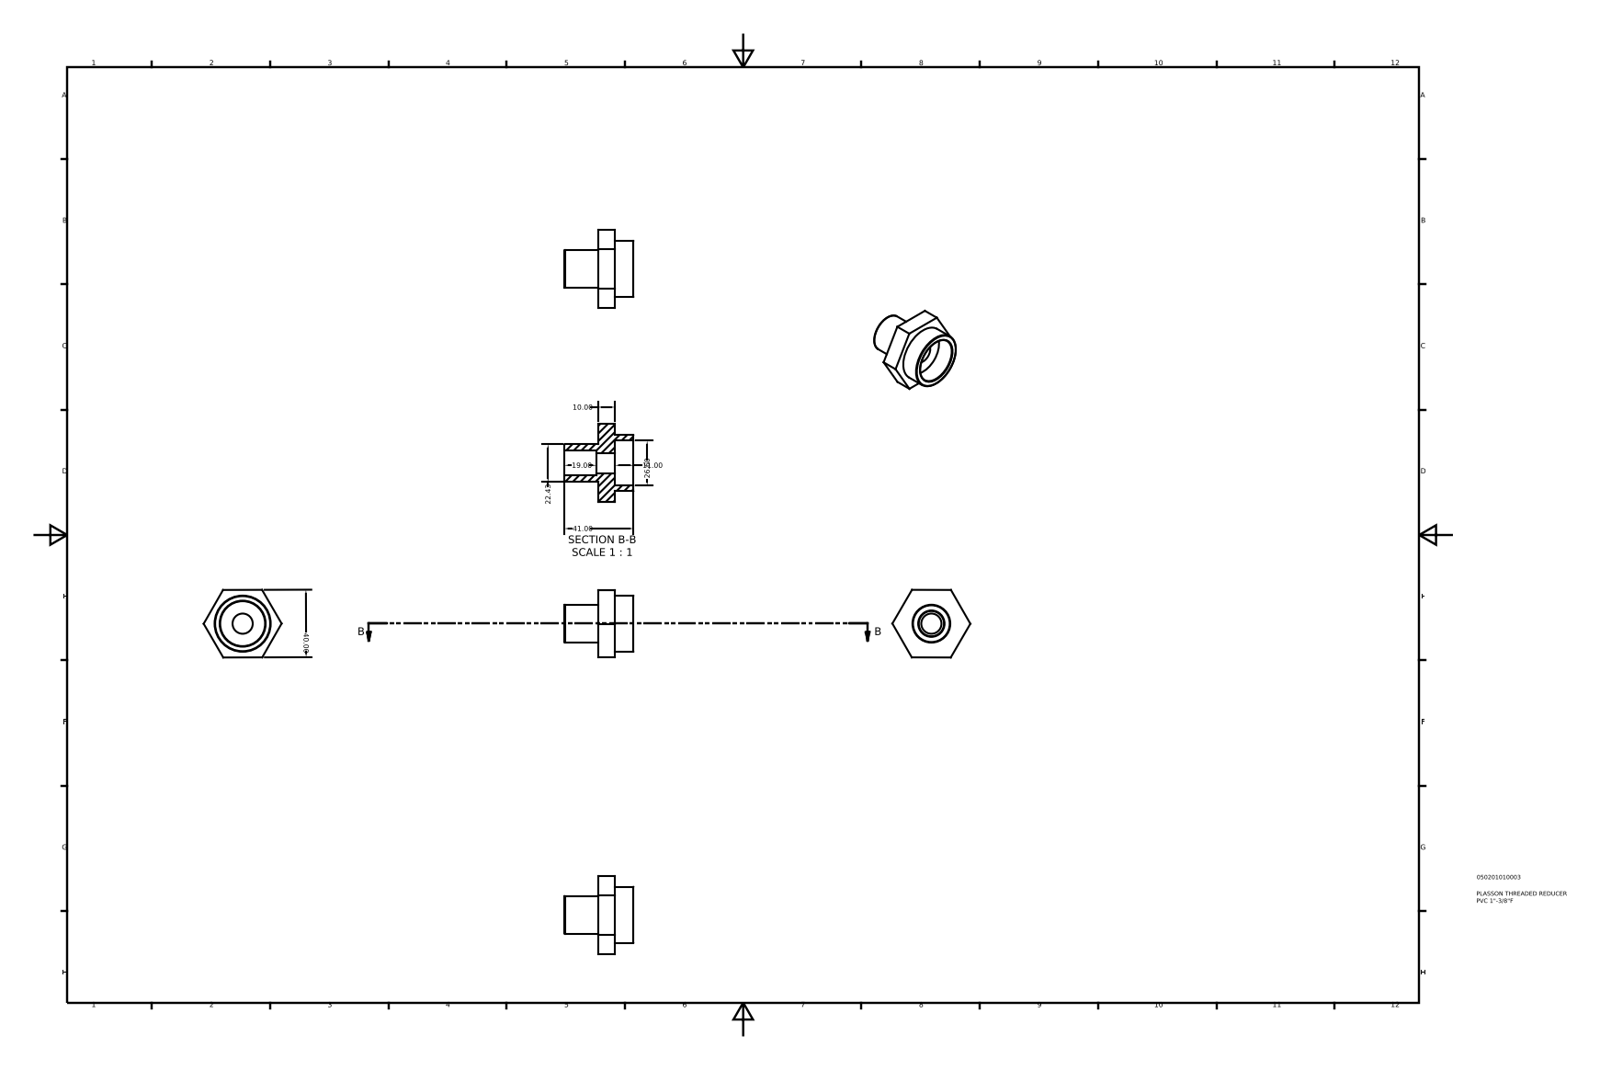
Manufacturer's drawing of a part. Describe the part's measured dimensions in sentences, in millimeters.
The part is named "050201010003". Its 3-D file was written by "Autodesk Inventor 2015 (AUTOMOTIVE_DESIGN)". It is 1 solid with 21 faces: 12 planar, 5 cylindrical and 4 other. Overall it measures 46.19 by 41 by 40.07 millimeters. Its volume is 20 616 cubic millimeters and its surface area 8 672 square millimeters. Round holes: 1 of diameter 11.96, 1 of diameter 14.95, 1 of diameter 26.6. Round bosses or shafts: 1 of diameter 33.25, 1 of diameter 22.43. The main face-to-face distances are 10, 40.02, 11, 21, 40, 20, 30, 41, 19, 1.
